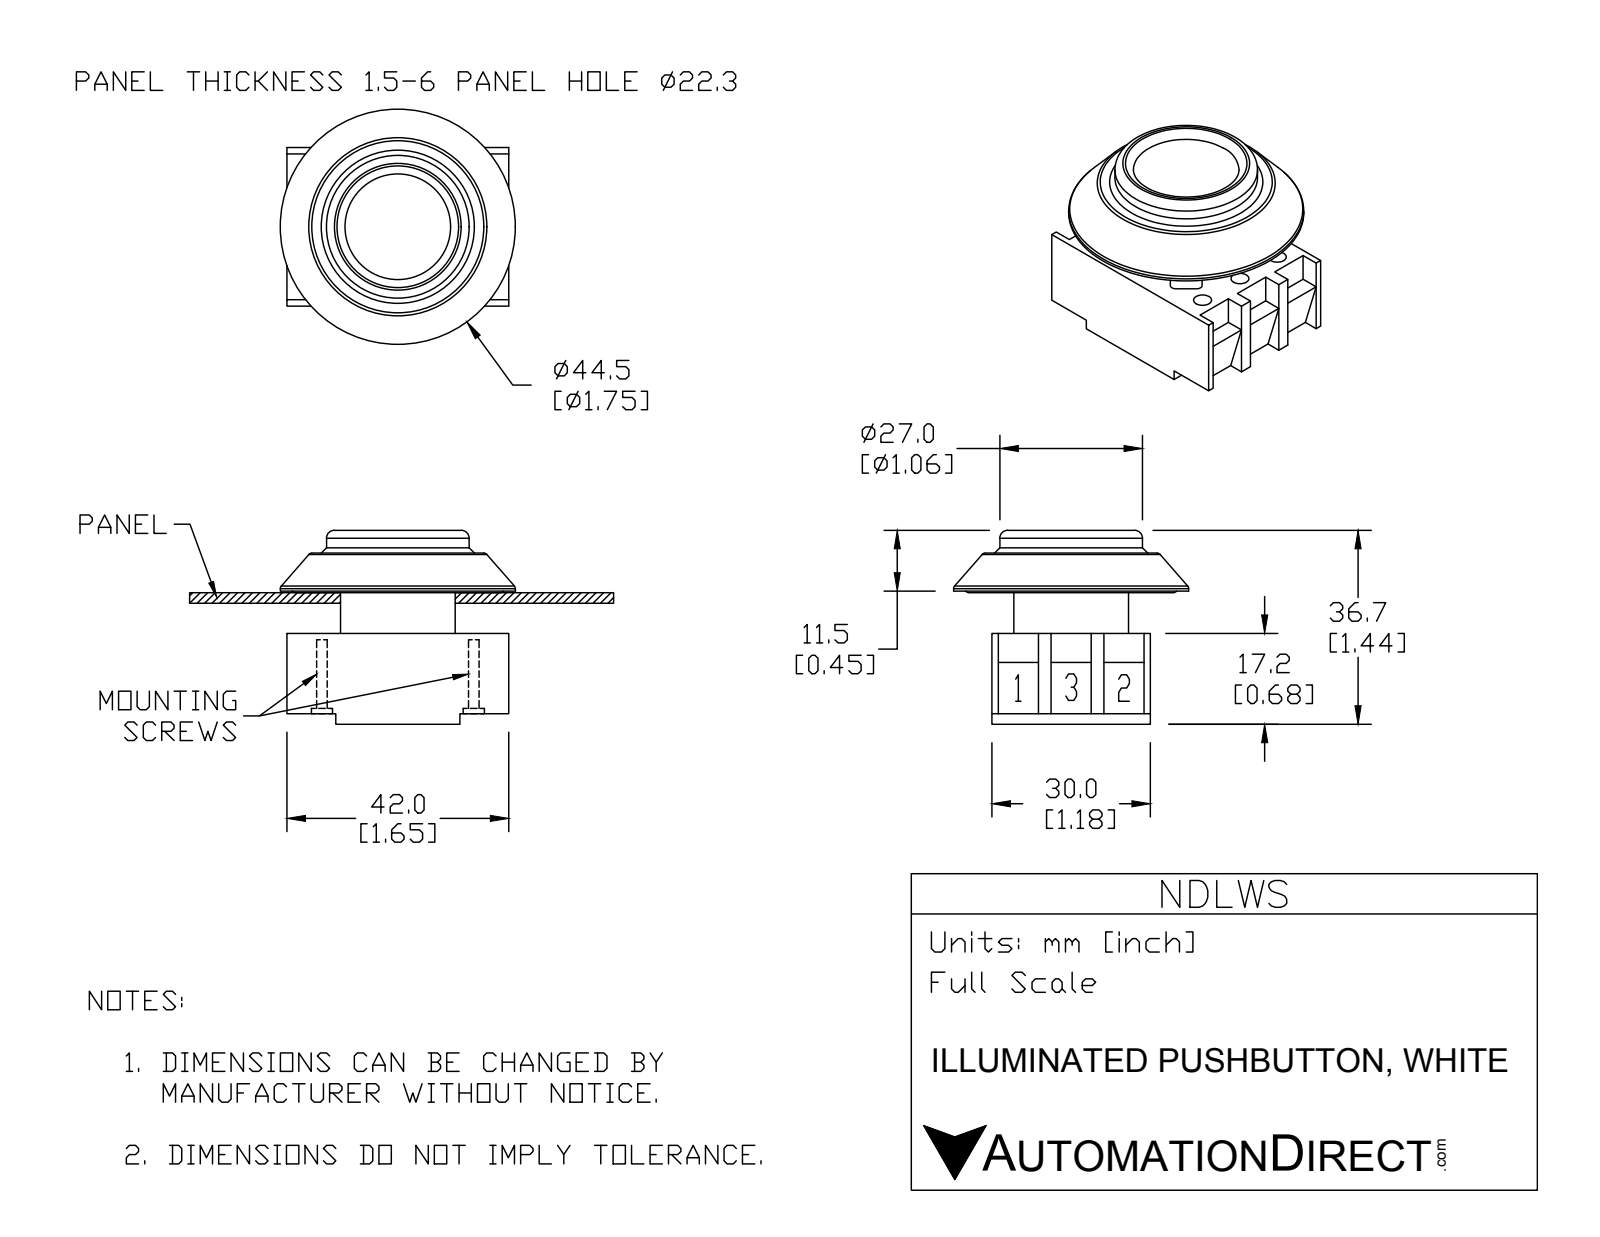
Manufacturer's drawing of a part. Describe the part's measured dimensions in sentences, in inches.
The part is named "NDLWS". Its 3-D file was written by "SolidWorks 2015 (AUTOMOTIVE_DESIGN)". It is 7 solids with 217 faces: 127 planar, 65 cylindrical and 25 other. Overall it measures 1.752 by 1.752 by 1.445 inches. Its volume is 1.533 cubic inches and its surface area 25.91 square inches. Round holes: 6 of diameter 0.134, 6 of diameter 0.197, 1 of diameter 0.492. Round bosses or shafts: 2 of diameter 0.181, 2 of diameter 0.157, 1 of diameter 1.752, 1 of diameter 1.063, 1 of diameter 0.854. Partial cylindrical surfaces (rounded edges, fillets, slot ends): 8 of radius 0.039, 5 of radius 0.343, 1 of radius 0.433. The main face-to-face distances are 0.283, 0.598, 1.181, 0.394, 0.315, 0.295, 0.303, 0.406, 0.709, 0.913. The hole center spacings are 0.394, 0.69, 1.199, 1.132, 0.566, 0.787, 1.379.
